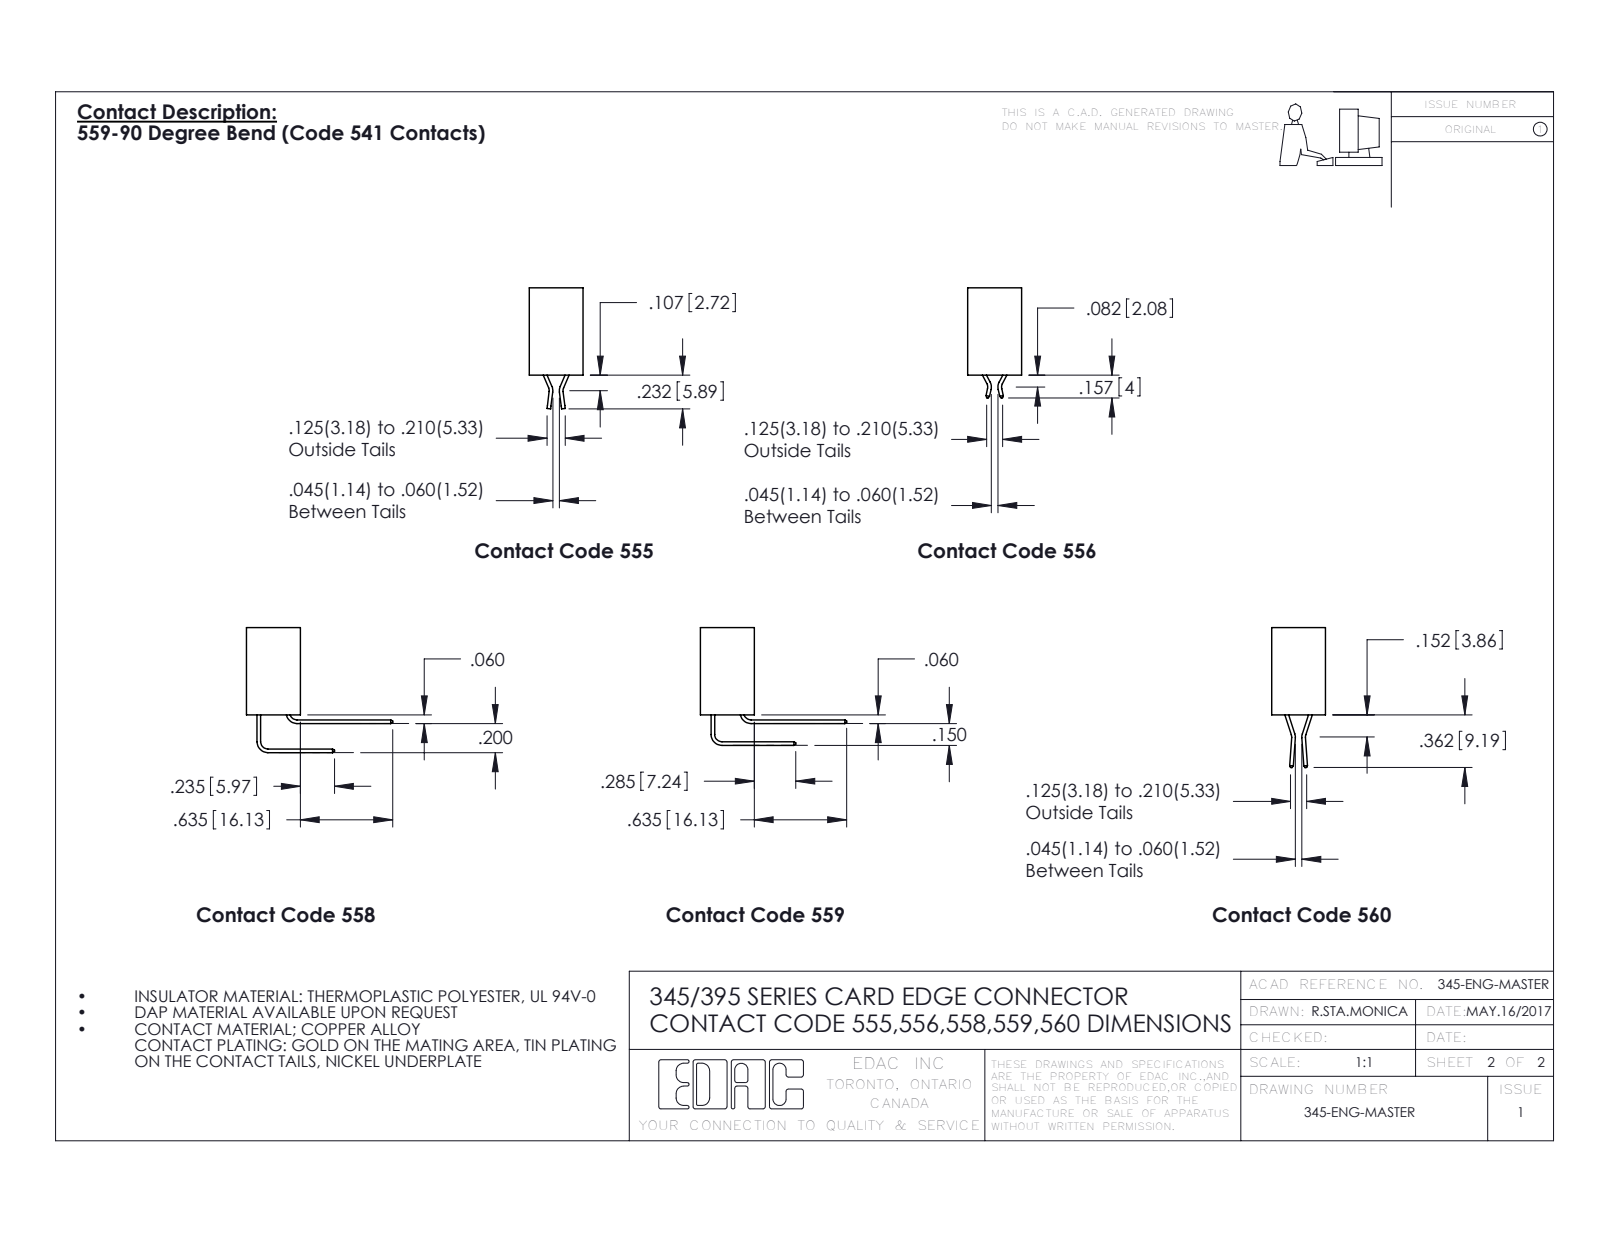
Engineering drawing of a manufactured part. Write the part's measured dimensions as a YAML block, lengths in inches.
part_name: "395-015-559-612; 345-292-001_558 559 Tail - 1; 345 Part_0.170 Offset - Side Mount"
step_written_by: "SolidWorks 2016 (CONFIG_CONTROL_DESIGN)"
units: inches
bodies: {solids: 16, faces: 1030, planar: 714, cylindrical: 316, other: 0}
overall_size: [2.335, 1.005, 0.659]
volume: 0.321
surface_area: 10.7
round_holes:
  - {diameter: 0.128, count: 2}
  - {diameter: 0.064, count: 1}
partial_cylinders:
  - {radius: 0.006, count: 30}
  - {radius: 0.01, count: 22}
  - {radius: 0.007, count: 6}
  - {radius: 0.031, count: 6}
  - {radius: 0.026, count: 3}
  - {radius: 0.031, count: 2}
  - {radius: 0.04, count: 2}
  - {radius: 0.014, count: 1}
face_to_face_distances: [0.37, 0.072, 0.298, 0.2, 0.098, 0.272, 0.025, 0.1, 0.225, 0.15]
hole_center_spacings: [2.075]
